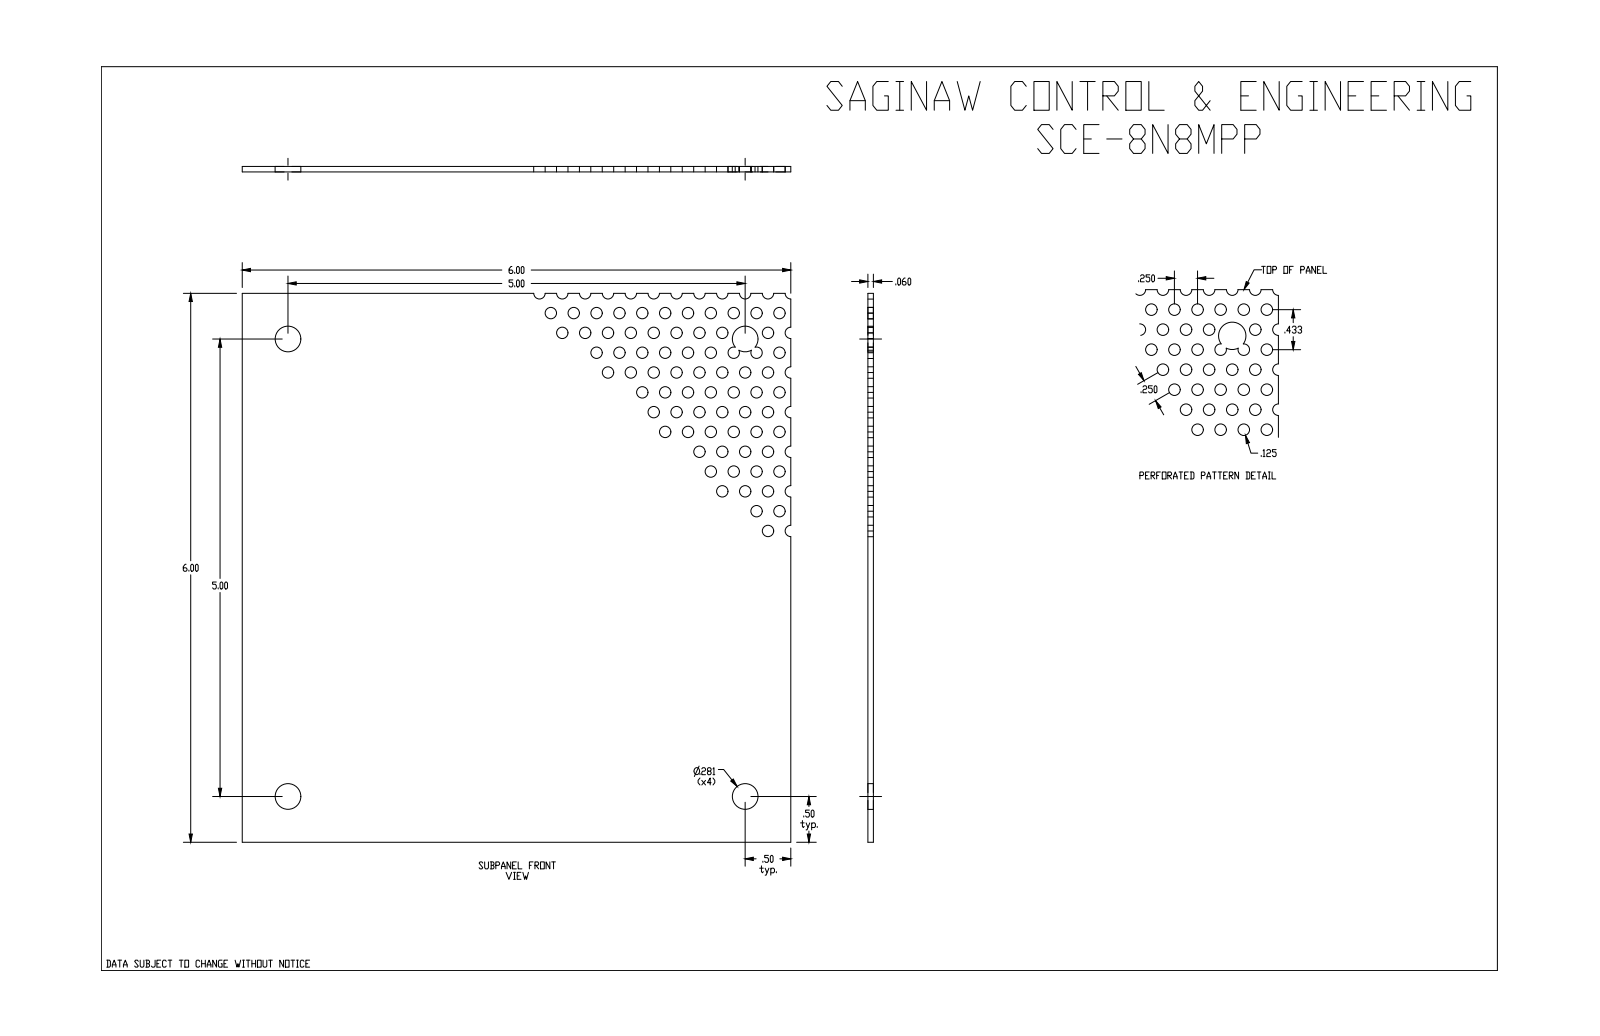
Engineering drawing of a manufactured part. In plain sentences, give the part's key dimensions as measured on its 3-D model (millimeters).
The part is named "SCE-8N8MPP". Its 3-D file was written by "SolidWorks 2019 (CONFIG_CONTROL_DESIGN)". It is 1 solid with 116 faces: 23 planar, 93 cylindrical and 0 other. Overall it measures 152.4 by 152.4 by 1.5 millimeters. Its volume is 34 200 cubic millimeters and its surface area 47 050 square millimeters. Round holes: 46 of diameter 3.2, 24 of diameter 3.2, 4 of diameter 7.1. Partial cylindrical surfaces (rounded edges, fillets, slot ends): 11 of radius 1.6, 7 of radius 1.6. The main face-to-face distances are 1.5, 152.4. The hole center spacings are 6.4, 16.8, 12.7, 11, 11, 33.6, 27.7, 19.1.
